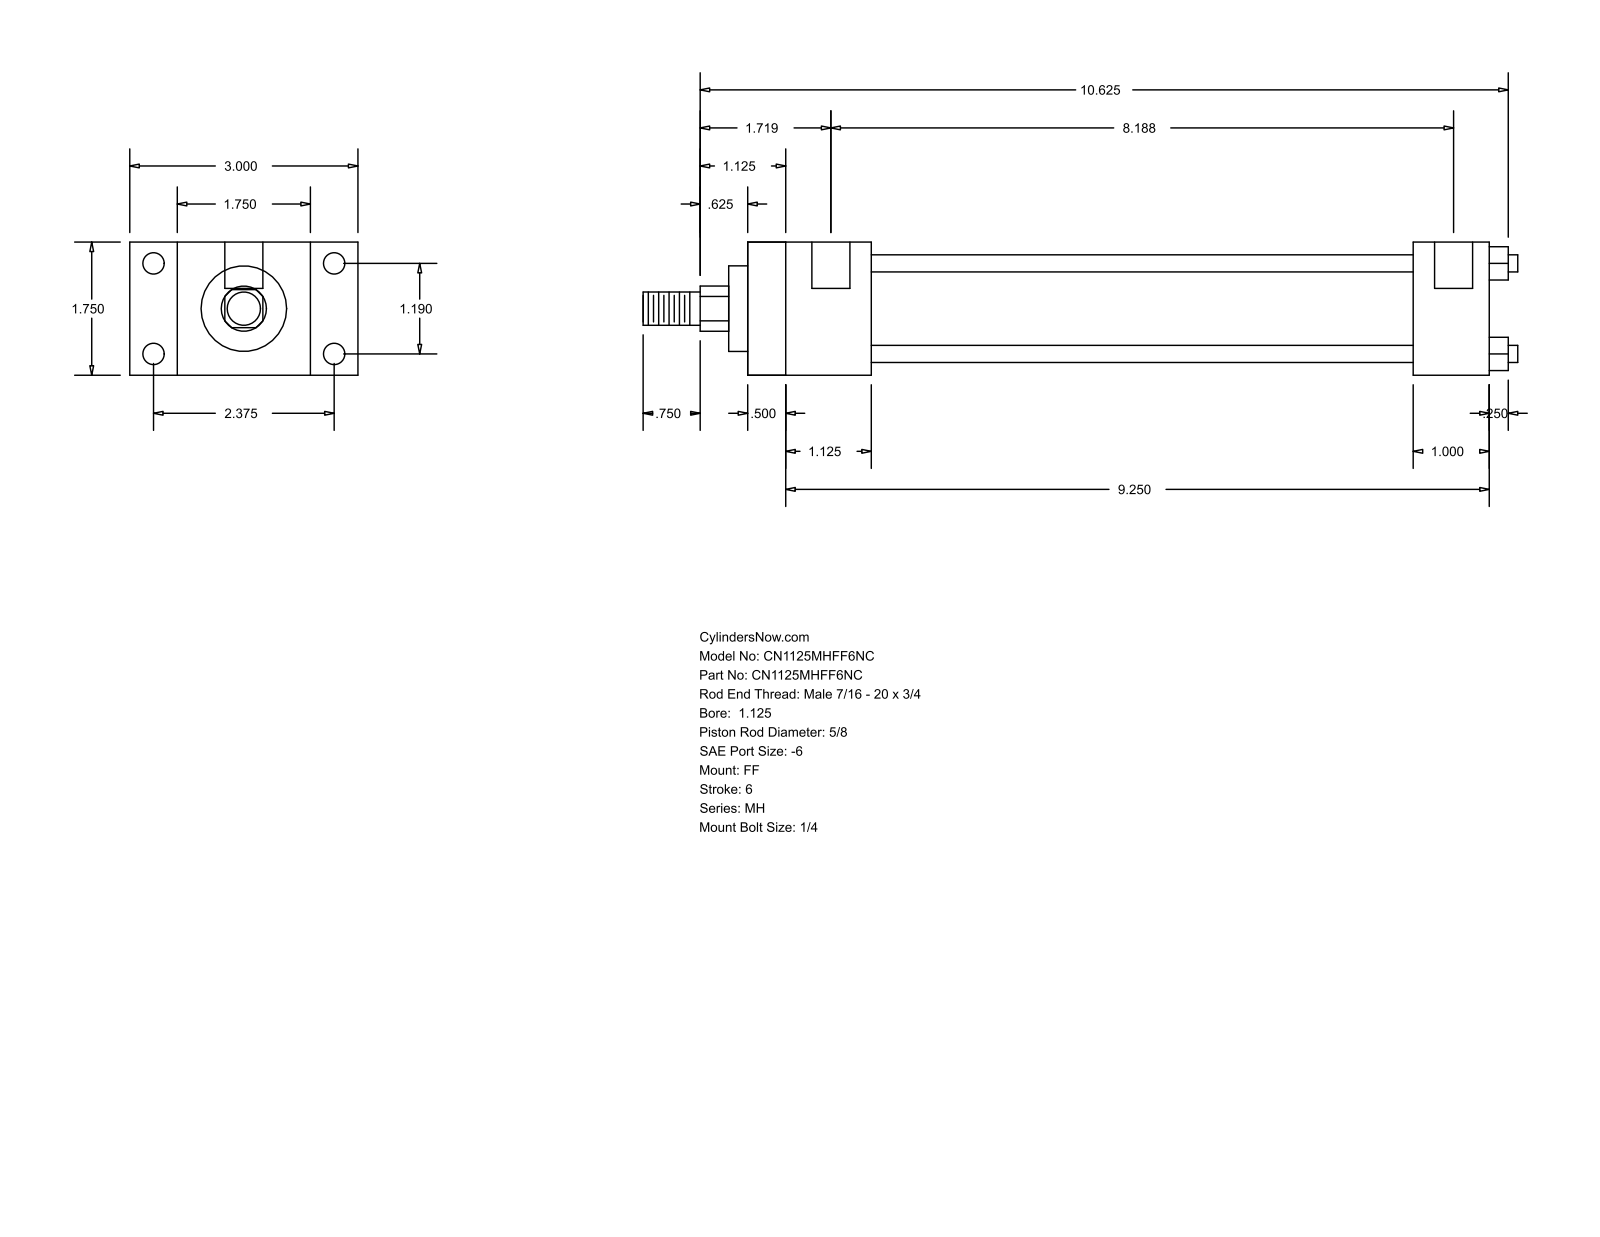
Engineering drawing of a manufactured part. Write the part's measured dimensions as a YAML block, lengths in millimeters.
part_name: "MH_FF__0112_0.625"
step_written_by: "GSSL Pune (CONFIG_CONTROL_DESIGN)"
units: millimeters
bodies: {solids: 0, faces: 92, planar: 64, cylindrical: 28, other: 0}
overall_size: [292.1, 76.2, 44.45]
round_holes:
  - {diameter: 5.56, count: 4}
  - {diameter: 7.14, count: 4}
  - {diameter: 12.7, count: 2}
round_bosses_or_shafts:
  - {diameter: 5.71, count: 4}
  - {diameter: 34.92, count: 1}
  - {diameter: 28.57, count: 1}
  - {diameter: 15.88, count: 1}
  - {diameter: 11.11, count: 1}
partial_cylinders:
  - {radius: 7.54, count: 1}
face_to_face_distances: [44.46, 247.64, 15.87, 12.69, 234.95, 28.58, 60.33, 25.4, 41.27, 222.24]
hole_center_spacings: [30.22, 60.32, 67.47, 204.79, 3.17, 207.96]
